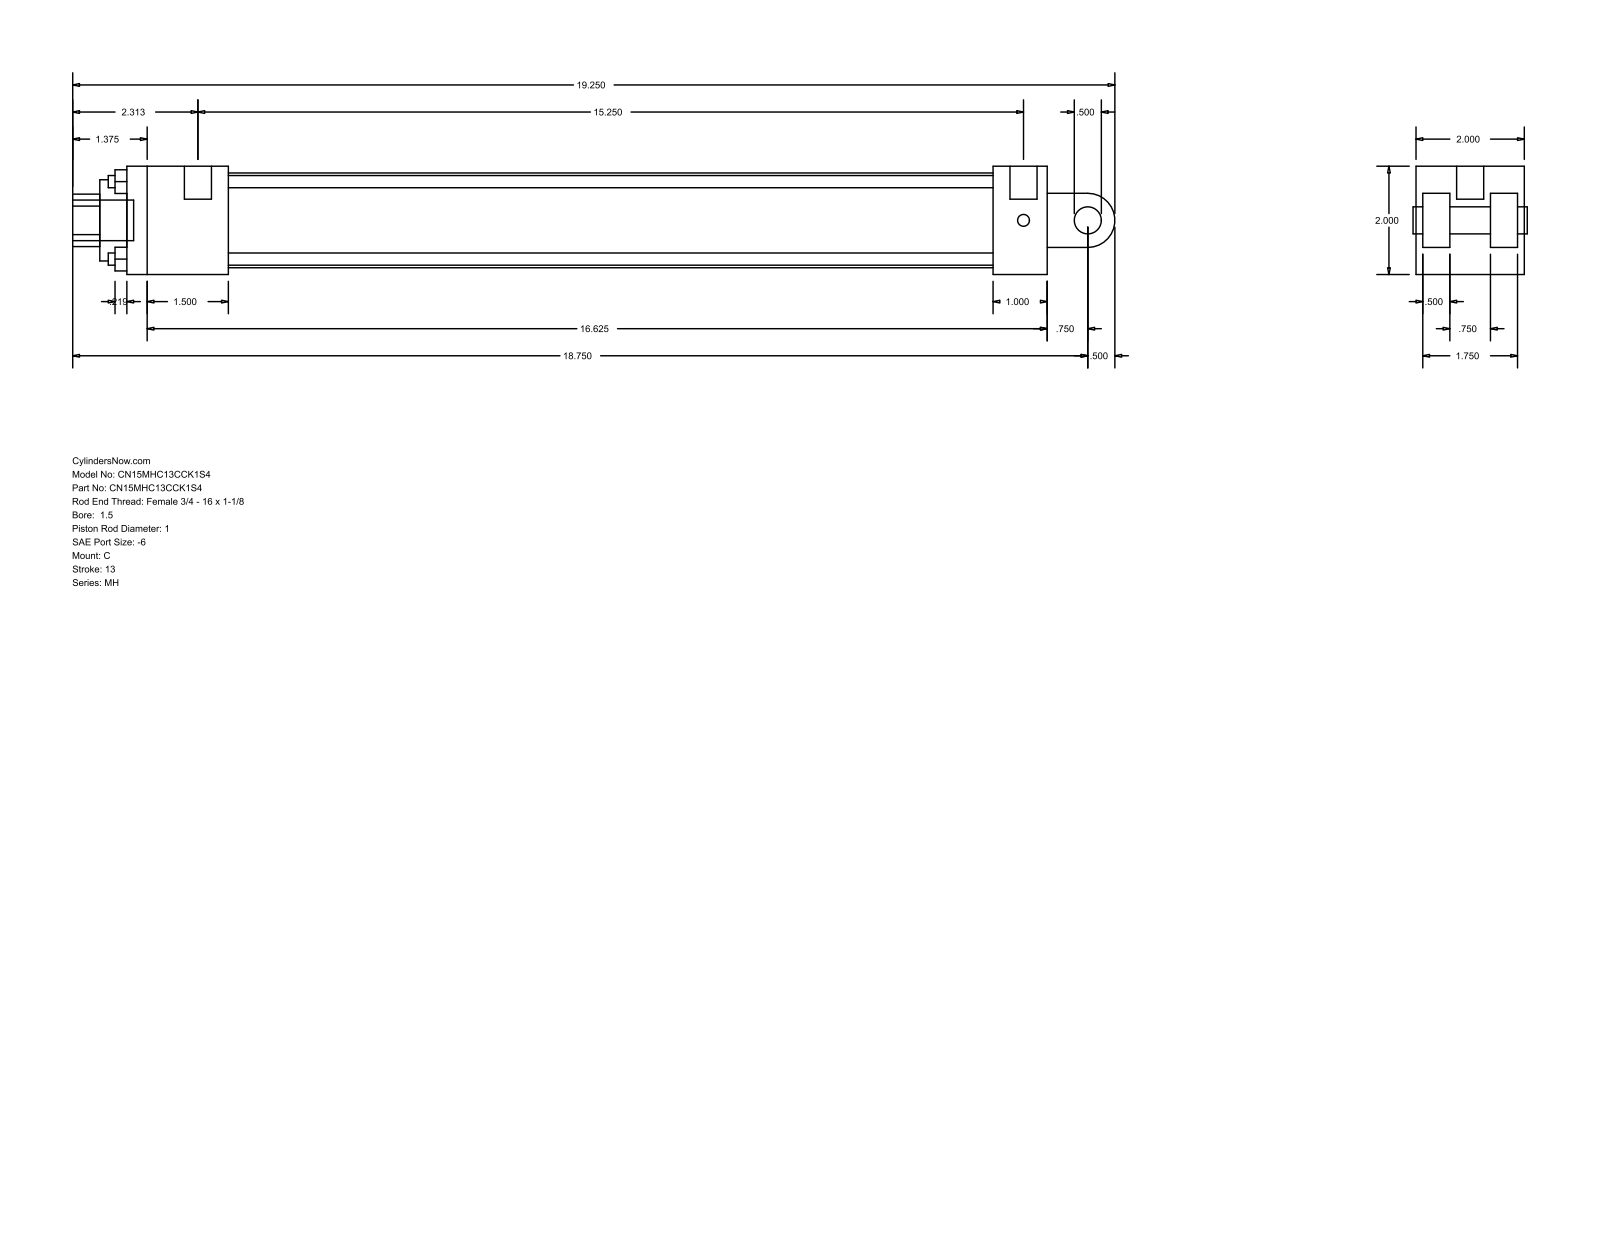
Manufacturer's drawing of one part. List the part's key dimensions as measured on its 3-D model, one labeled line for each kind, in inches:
Part name (STEP PRODUCT): MH_C__0150_1
STEP written by: GSSL Pune (CONFIG_CONTROL_DESIGN)
Units: inches
Bodies: 0 solids, 99 faces (70 planar, 29 cylindrical, 0 other)
Overall size (bounding box): 19.25 × 2 × 2
Round holes (diameter × count): ⌀0.225 ×4, ⌀0.219 ×2, ⌀0.5 ×1, ⌀1 ×1, ⌀1.5 ×1, ⌀1.75 ×1
Round bosses / shafts (diameter × count): ⌀0.5 ×2, ⌀0.219 ×2, ⌀0.75 ×1
Partial cylindrical surfaces — rounded edges, fillets, slot ends (radius × count): R0.484 ×1, R0.5 ×1
Main face-to-face distances: 2, 0.5, 1.875, 0.125, 0.625, 1, 1.375, 1.25, 17, 1.5
Hole centre spacings: 1.011, 1.43, 2.022
